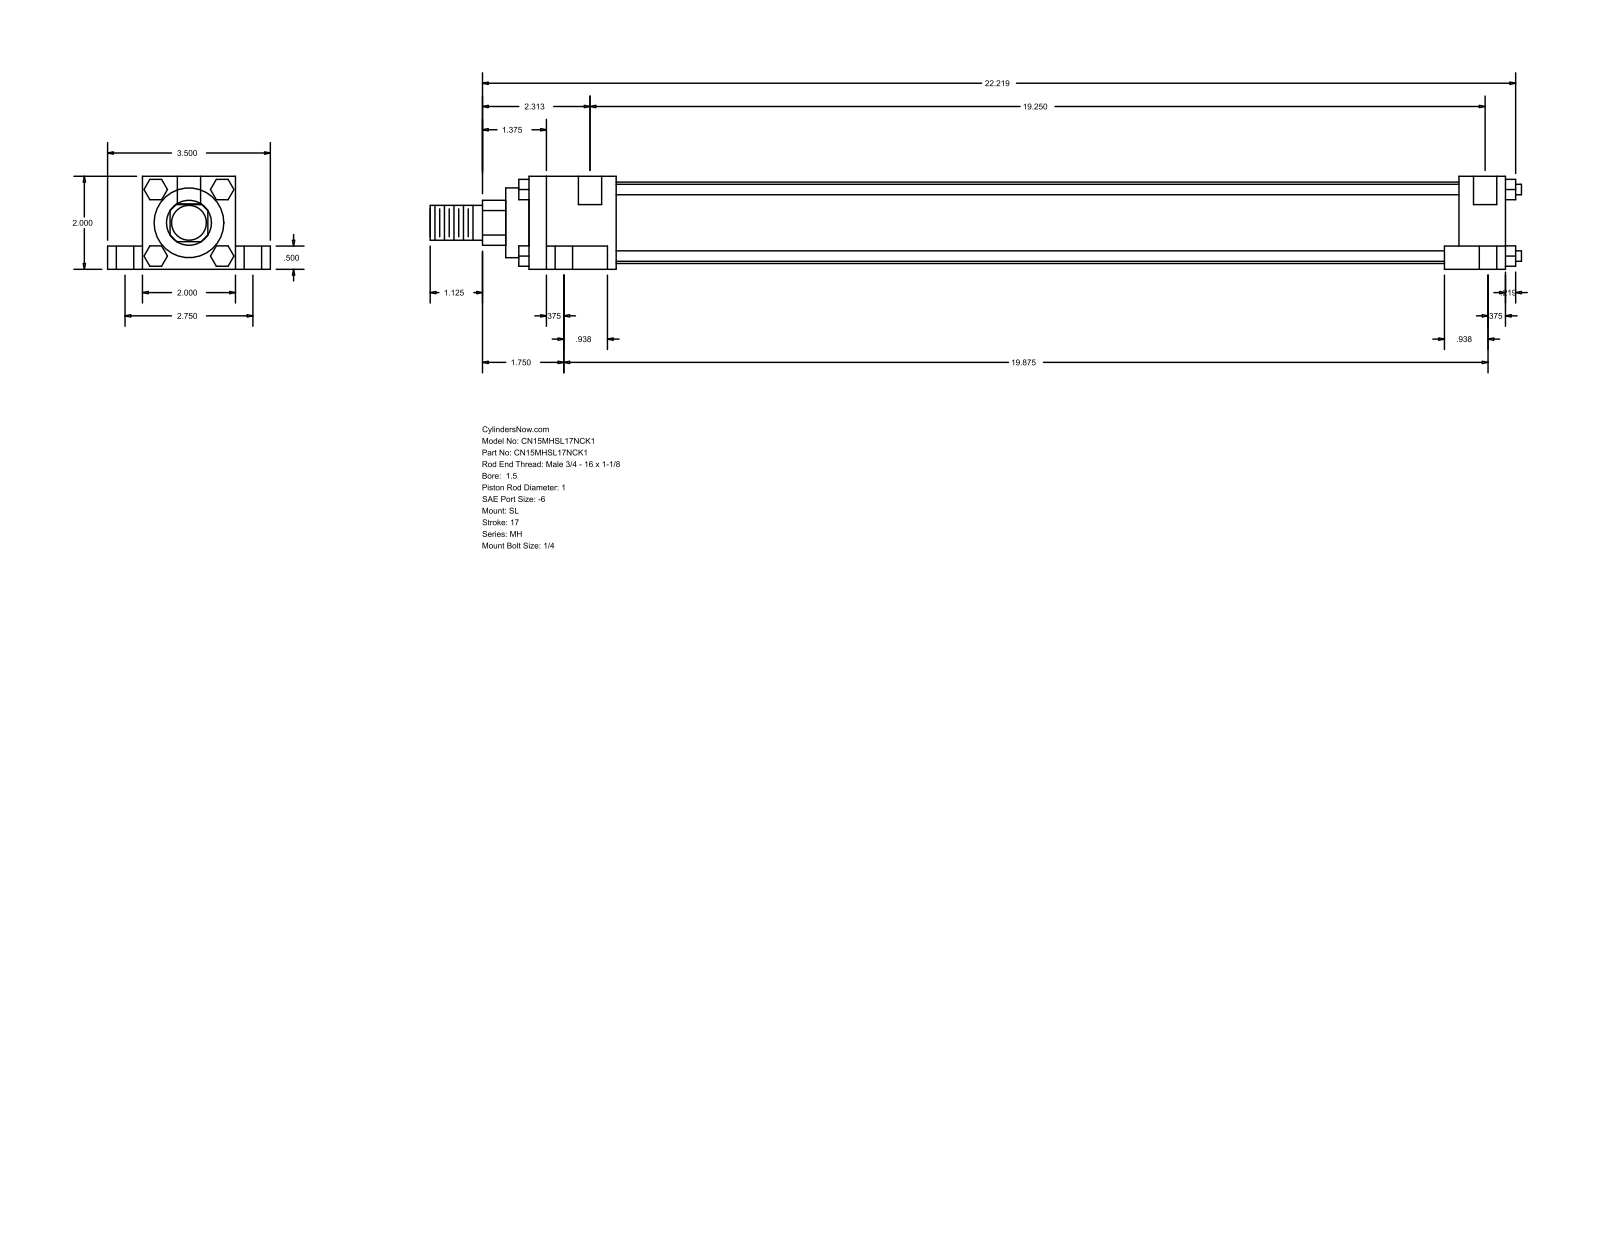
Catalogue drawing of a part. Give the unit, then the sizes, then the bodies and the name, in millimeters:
Units: millimetres
Overall size (bounding box): 596.11 × 88.9 × 50.8
Round holes (diameter × count): ⌀5.56 ×4, ⌀9.53 ×4, ⌀15.88 ×4, ⌀12.7 ×2
Round bosses / shafts (diameter × count): ⌀5.71 ×4, ⌀44.45 ×1, ⌀38.1 ×1, ⌀25.4 ×1, ⌀19.05 ×1
Partial cylindrical surfaces — rounded edges, fillets, slot ends (radius × count): R12.29 ×1
Main face-to-face distances: 50.8, 12.7, 38.1, 19.05, 69.85, 533.4, 25.4, 9.52, 33.34, 490.54
Hole centre spacings: 34.96, 36.64, 37.73, 69.84, 491.77, 492.13, 494.94, 504.45
Bodies: 0 solids, 148 faces (112 planar, 36 cylindrical, 0 other)
Part name (STEP PRODUCT): MH_SL__0150_1
STEP written by: GSSL Pune (CONFIG_CONTROL_DESIGN)
